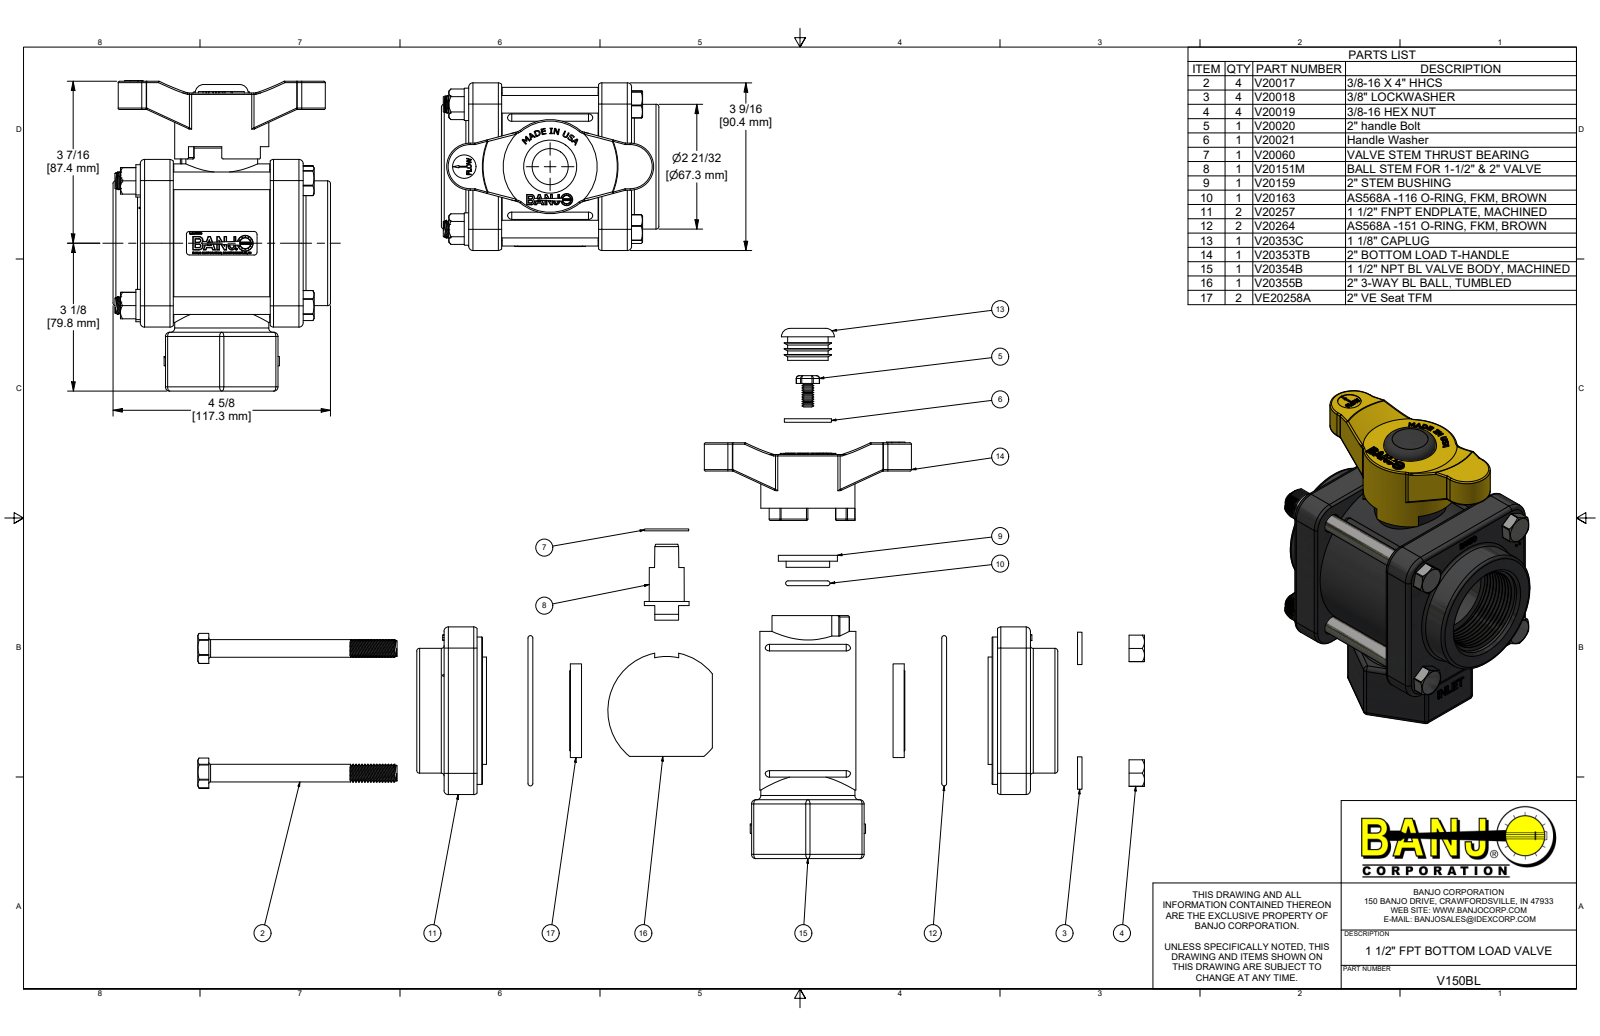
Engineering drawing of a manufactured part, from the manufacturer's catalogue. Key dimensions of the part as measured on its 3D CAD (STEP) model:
Part name (STEP PRODUCT): V150BL; 050DECAL; V20017; V20018 (+8 more)
STEP written by: Autodesk Inventor 2019 (AUTOMOTIVE_DESIGN)
Units: inches
Bodies: 30 solids, 3009 faces (1458 planar, 538 cylindrical, 1013 other)
Overall size (bounding box): 6.595 × 4.66 × 3.56
Volume: 39.19 in³ · Surface area: 317.7 in²
Round holes (diameter × count): ⌀0.307 ×4, ⌀0.385 ×4, ⌀0.406 ×4, ⌀1.46 ×2, ⌀1.5 ×2, ⌀0.172 ×1, ⌀0.196 ×1, ⌀0.227 ×1, ⌀0.244 ×1, ⌀0.281 ×1, ⌀0.32 ×1, ⌀0.321 ×1
Round bosses / shafts (diameter × count): ⌀0.324 ×60, ⌀0.687 ×4, ⌀0.375 ×4, ⌀3.37 ×1, ⌀3.13 ×1, ⌀2.9 ×1, ⌀2.65 ×1, ⌀2.26 ×1
Partial cylindrical surfaces — rounded edges, fillets, slot ends (radius × count): R0.03 ×56, R0.09 ×38, R0.06 ×8, R0.075 ×8, R0.162 ×8, R0.062 ×4, R0.125 ×4, R0.32 ×4
Main face-to-face distances: 0.7, 2.8, 3.56, 3.5, 0.815, 0.35, 2.685, 0.115, 1.985, 0.683
Hole centre spacings: 1.872, 2.648, 3.745, 0.783, 1.825, 2.285
